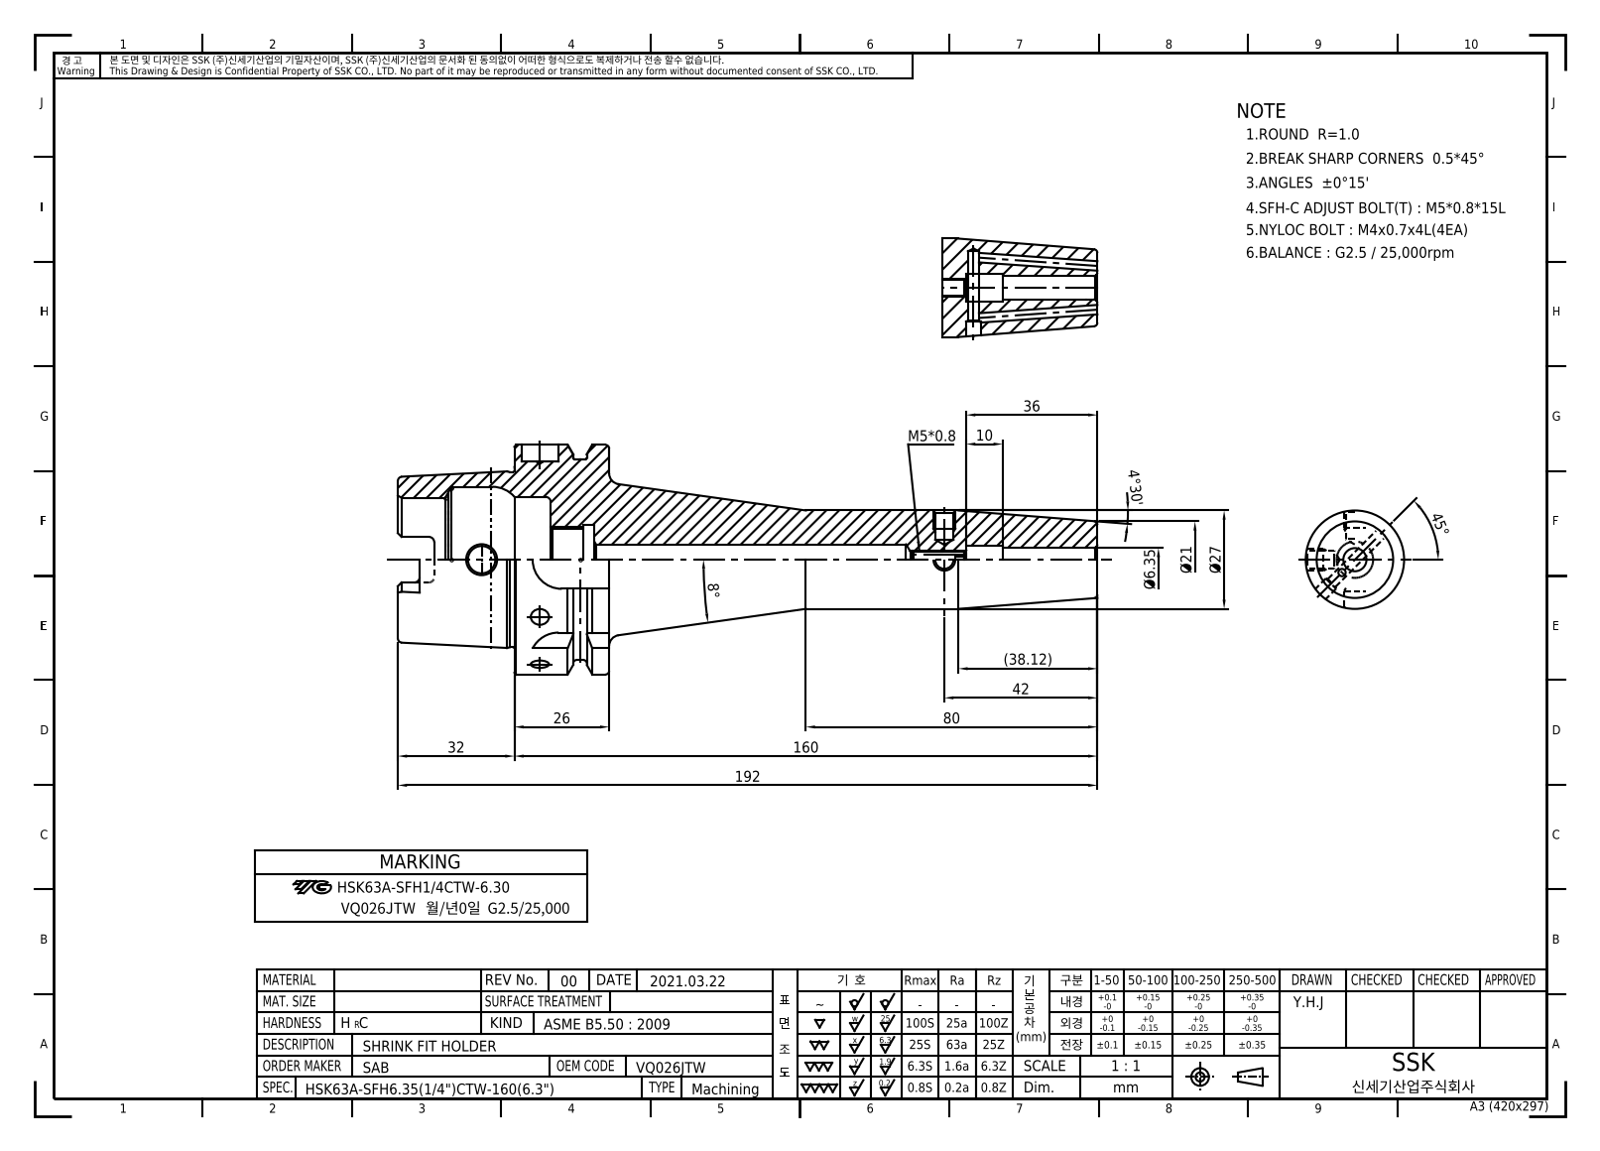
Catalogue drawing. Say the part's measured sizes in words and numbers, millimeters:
The part is named "LO-HSK63A-SFH6.35CTW-160". Its 3-D file was written by "Autodesk Inventor 2022 (AUTOMOTIVE_DESIGN)". It is 1 solid with 116 faces: 42 planar, 34 cylindrical and 40 other. Overall it measures 192 by 63 by 63 millimeters. Its volume is 168 898 cubic millimeters and its surface area 36 589 square millimeters. Round holes: 1 of diameter 4.3, 1 of diameter 6.35, 1 of diameter 7.5, 1 of diameter 7.55, 1 of diameter 8, 1 of diameter 10, 1 of diameter 16.92, 1 of diameter 19, 1 of diameter 34, 1 of diameter 40. Round bosses or shafts: 1 of diameter 63, 1 of diameter 55, 1 of diameter 48.04, 1 of diameter 27. Partial cylindrical surfaces (rounded edges, fillets, slot ends): 6 of radius 1.5, 4 of radius 2.88, 4 of radius 8. The main face-to-face distances are 26, 10, 16, 32, 42, 58, 150, 160, 134, 192.
